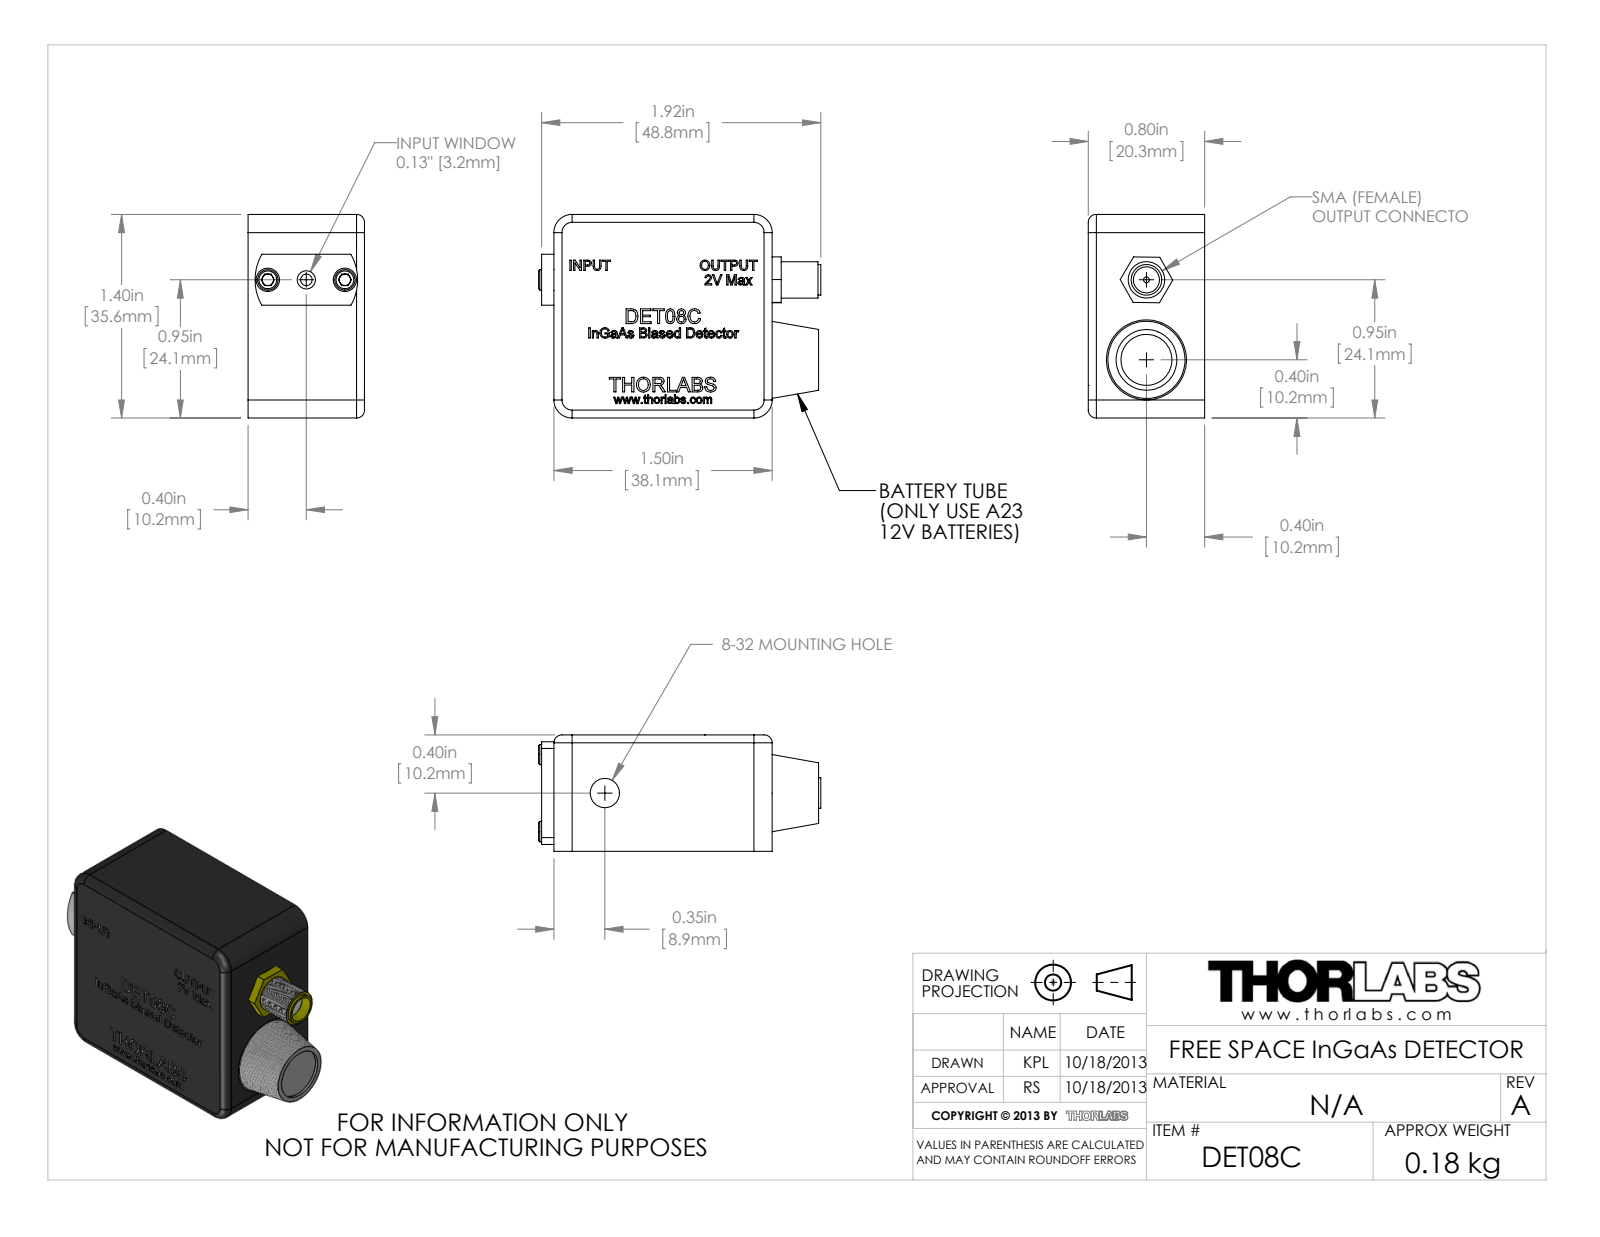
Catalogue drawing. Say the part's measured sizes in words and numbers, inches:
The part is named "TTN020104; PCB 002; PCB 001; OSI PD (+8 more)". Its 3-D file was written by "SolidWorks 2012 (AUTOMOTIVE_DESIGN)". It is 15 solids with 1703 faces: 1000 planar, 179 cylindrical and 524 other. Overall it measures 1.941 by 1.4 by 0.8 inches. Its volume is 1.098 cubic inches and its surface area 23 square inches. Round holes: 6 of diameter 0.07, 4 of diameter 0.096, 4 of diameter 0.125, 4 of diameter 0.14, 2 of diameter 0.085, 2 of diameter 0.16, 1 of diameter 0.017, 1 of diameter 0.04, 1 of diameter 0.05, 1 of diameter 0.079, 1 of diameter 0.125, 1 of diameter 0.179. Round bosses or shafts: 6 of diameter 0.086, 4 of diameter 0.143, 3 of diameter 0.017, 2 of diameter 0.14, 1 of diameter 0.472, 1 of diameter 0.432, 1 of diameter 0.327, 1 of diameter 0.31. Partial cylindrical surfaces (rounded edges, fillets, slot ends): 12 of radius 0.125, 4 of radius 0.032, 4 of radius 0.055, 4 of radius 0.08, 4 of radius 0.095, 2 of radius 0.06, 2 of radius 0.1, 1 of radius 0.008. The main face-to-face distances are 0.063, 0.737, 0.8, 1.4, 0.5, 0.563, 0.237, 0.1, 0.55, 1.5. The hole center spacings are 1.698, 1.25, 0.265, 0.611, 1.15, 1.15, 1.25, 1.331.
